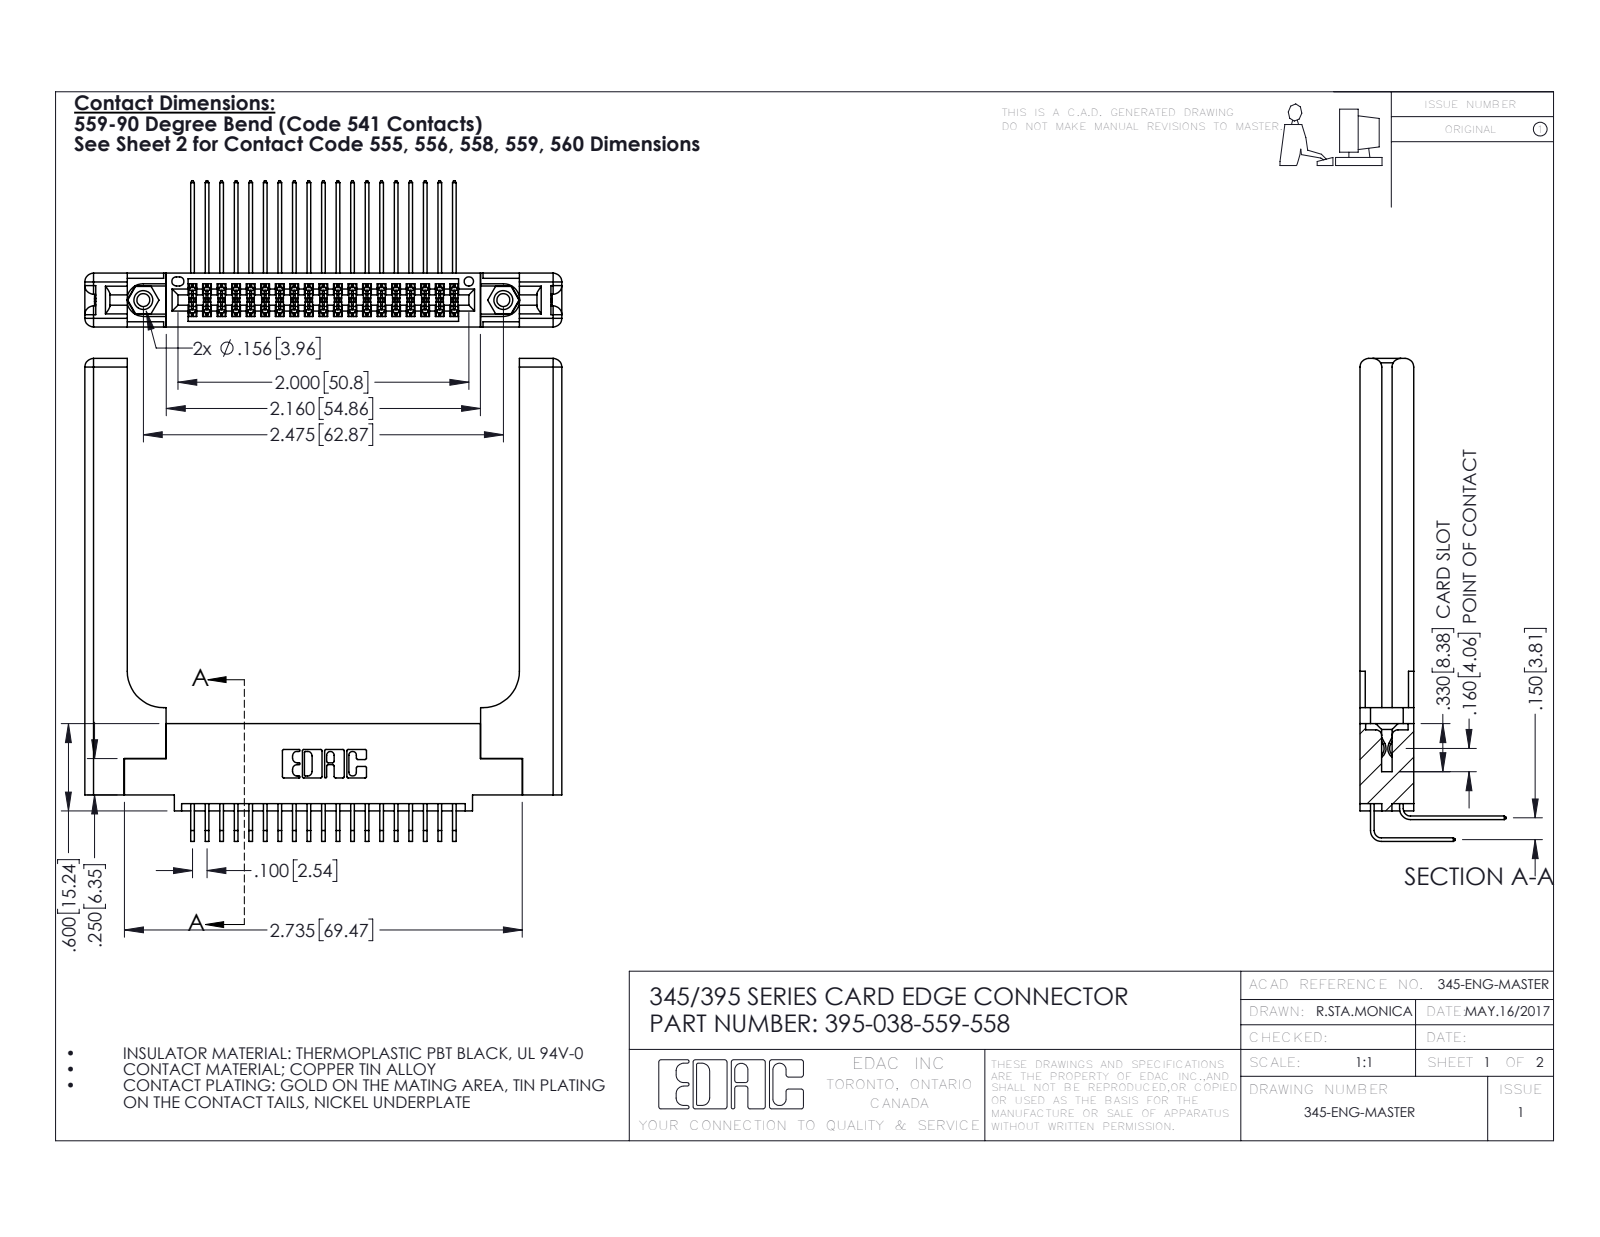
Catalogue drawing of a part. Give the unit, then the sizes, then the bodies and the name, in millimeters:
Units: millimetres
Overall size (bounding box): 84.3 × 83.3 × 25.5
Round holes (diameter × count): ⌀2.3 ×2, ⌀3.2 ×2, ⌀4 ×2, ⌀1.6 ×1
Round bosses / shafts (diameter × count): ⌀3.9 ×2
Partial cylindrical surfaces — rounded edges, fillets, slot ends (radius × count): R0.2 ×58, R0.3 ×22, R1.5 ×16, R0.2 ×6, R0.8 ×6, R0.7 ×3, R0.4 ×2, R0.5 ×2
Main face-to-face distances: 9.4, 1.8, 7.6, 3.8, 3.8, 2, 5.6, 5.1, 2.5, 6.9
Hole centre spacings: 6.9, 56.9, 62.9
Volume: 16 500 mm³ · Surface area: 17 590 mm²
Bodies: 43 solids, 2362 faces (1562 planar, 740 cylindrical, 60 other)
Part name (STEP PRODUCT): 345-250-001_345-250-001-102; 395-038-559-558; 345-220-058_345-220-058; 345-292-001_559 Tail - 2 (+2 more)
STEP written by: SolidWorks 2016 (CONFIG_CONTROL_DESIGN)
